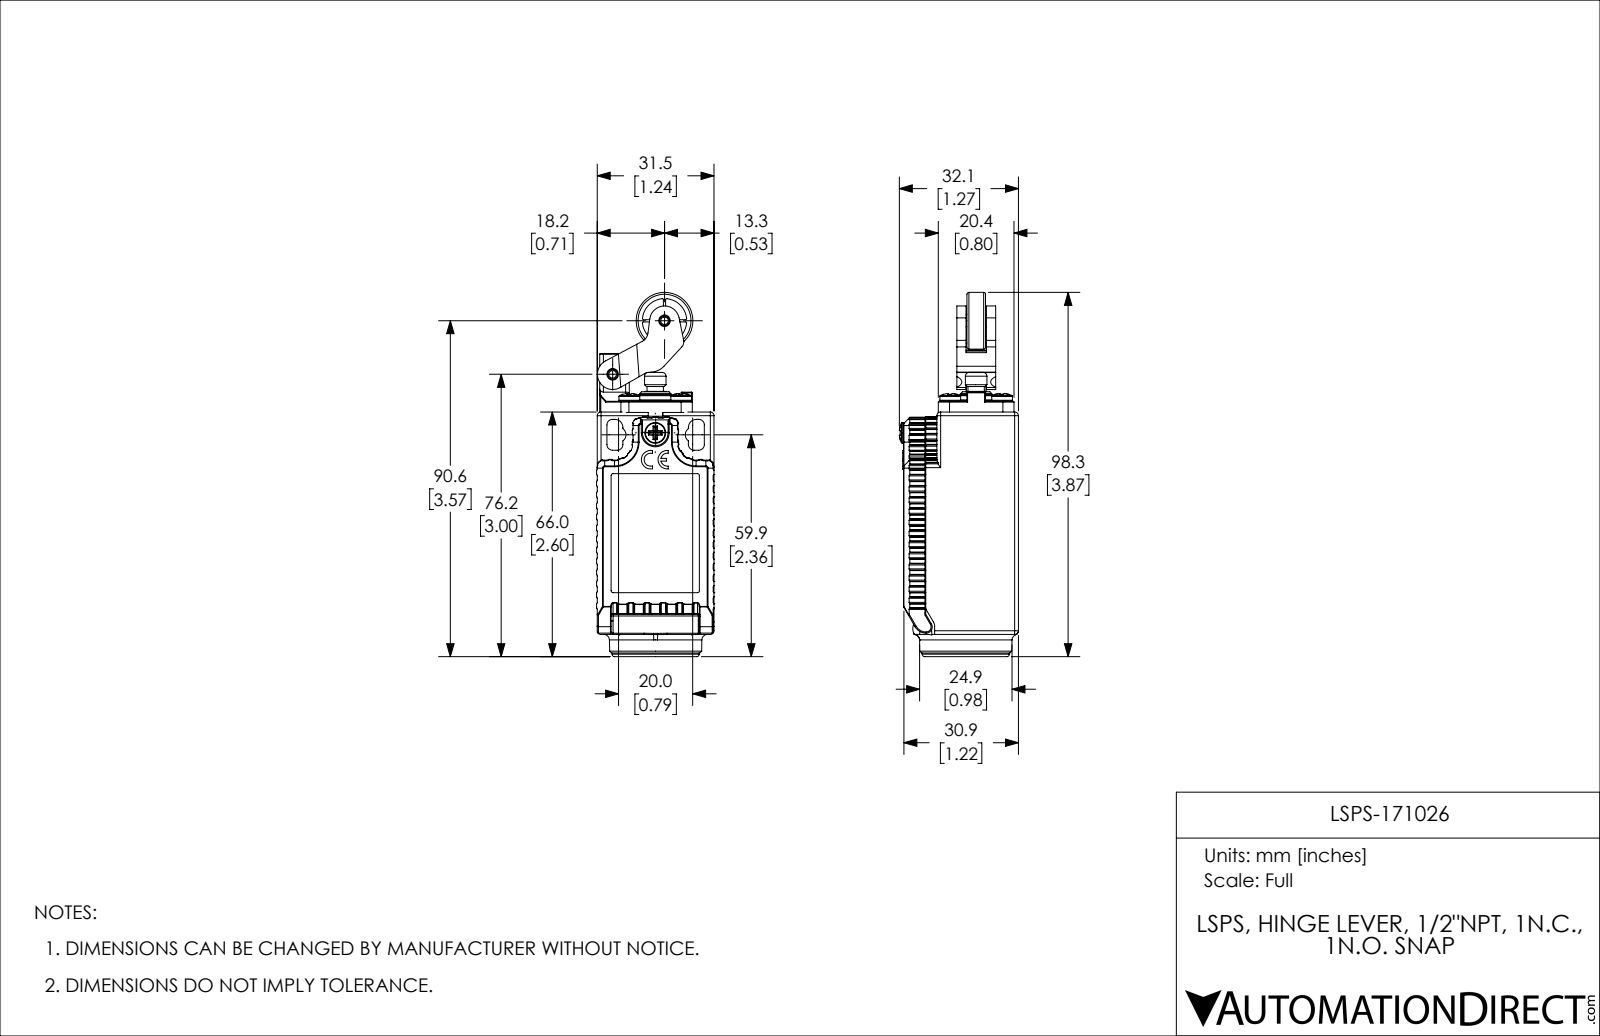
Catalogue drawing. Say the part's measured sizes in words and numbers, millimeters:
The part is named "171-LSPS-Hinge Lever (step format)". Its 3-D file was written by "SolidWorks 2013 (CONFIG_CONTROL_DESIGN)". It is 17 solids with 2586 faces: 1083 planar, 1124 cylindrical and 379 other. Overall it measures 98.25 by 32.13 by 31.7 millimeters. Its volume is 29 511 cubic millimeters and its surface area 31 274 square millimeters. Round holes: 5 of diameter 2.3, 4 of diameter 3.3, 4 of diameter 5.5, 2 of diameter 2.05, 2 of diameter 3.1, 2 of diameter 3.5, 2 of diameter 4, 1 of diameter 3.7, 1 of diameter 5, 1 of diameter 8, 1 of diameter 10, 1 of diameter 12. Round bosses or shafts: 5 of diameter 5.6, 5 of diameter 1.7, 2 of diameter 3.25, 1 of diameter 23.5, 1 of diameter 17.7, 1 of diameter 15.7, 1 of diameter 15.3, 1 of diameter 14.4. Partial cylindrical surfaces (rounded edges, fillets, slot ends): 159 of radius 0.5, 130 of radius 0.2, 124 of radius 0.1, 73 of radius 0.3, 34 of radius 1, 32 of radius 0.34, 28 of radius 0.25, 17 of radius 2. The main face-to-face distances are 2.25, 29.25, 31.5, 1.6, 1, 3, 26.8, 25.2, 27, 29.8. The hole center spacings are 9.9, 14, 19.8, 13.9, 14.1, 7.76, 8.22, 9.76.
